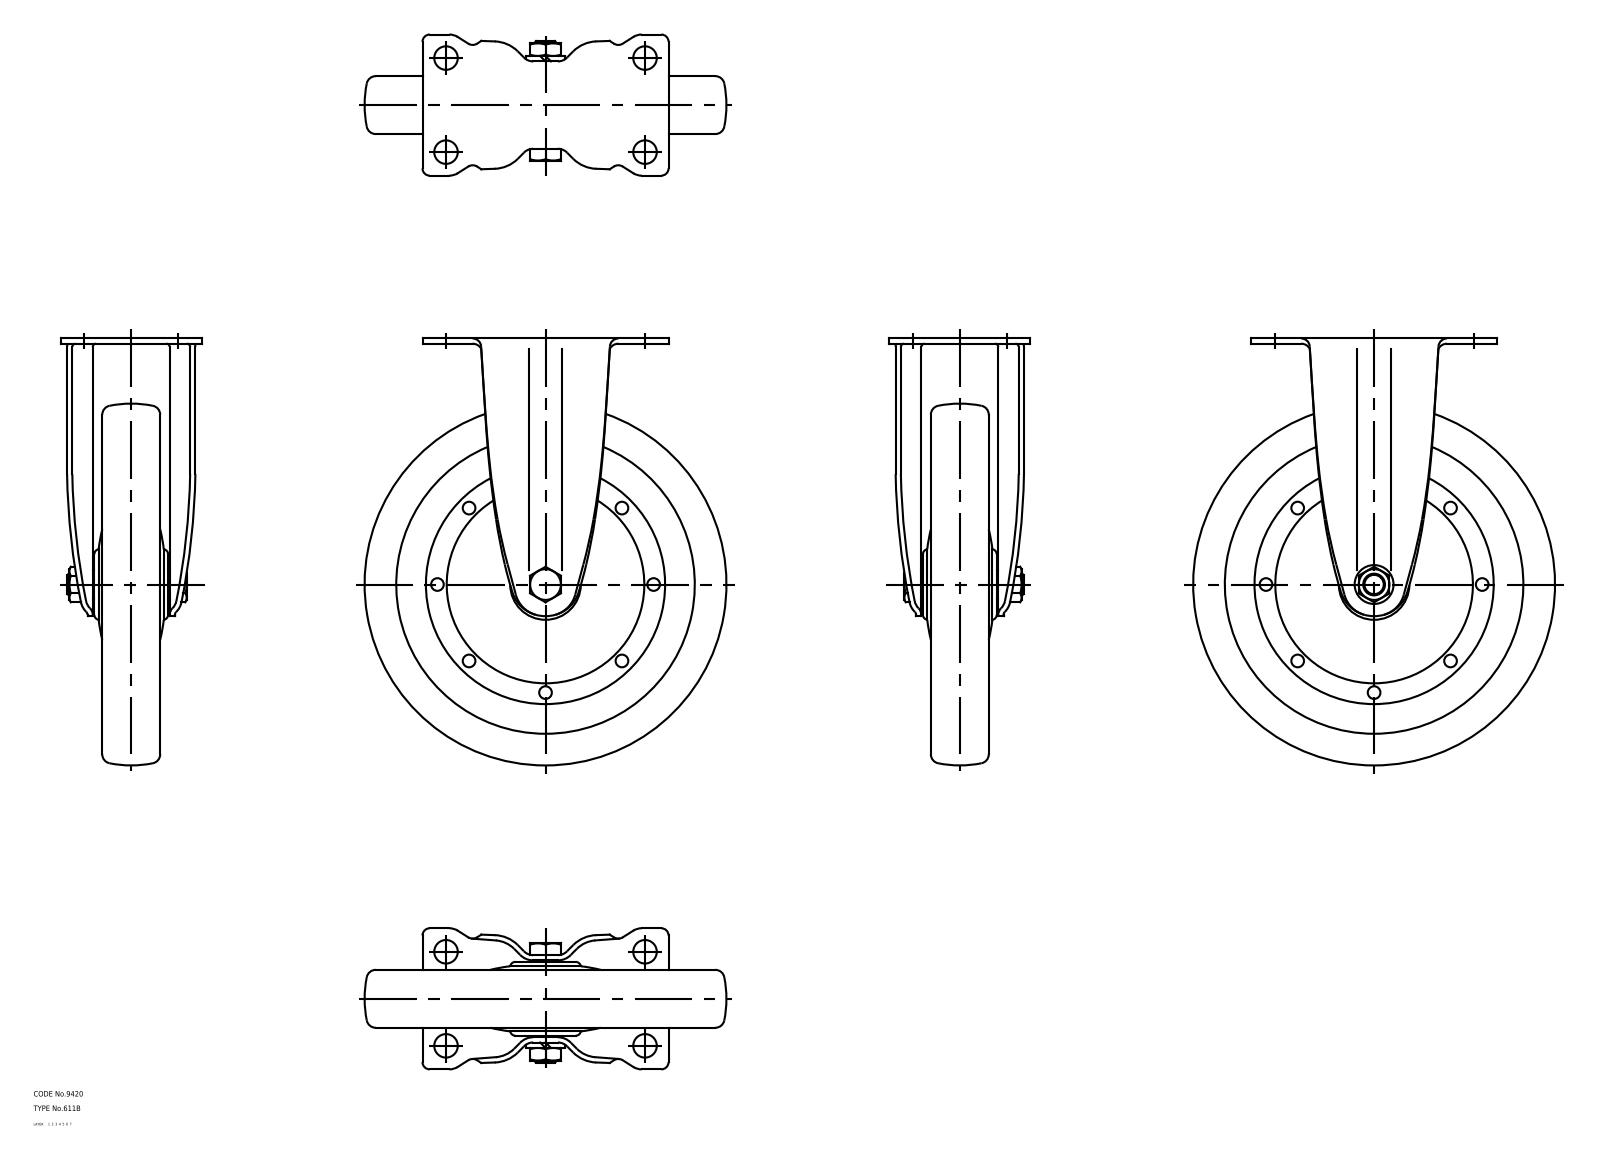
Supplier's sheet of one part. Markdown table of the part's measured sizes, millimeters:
| quantity | value |
| --- | --- |
| part name | 67125866; 67125879; 67125892 |
| STEP written by | CADfix (AUTOMOTIVE_DESIGN) |
| units | millimeters |
| bodies | 3 solids, 266 faces (0 planar, 0 cylindrical, 266 other) |
| overall size | 236 × 200 × 78 |
| volume | 931 634 mm³ |
| surface area | 144 917 mm² |
